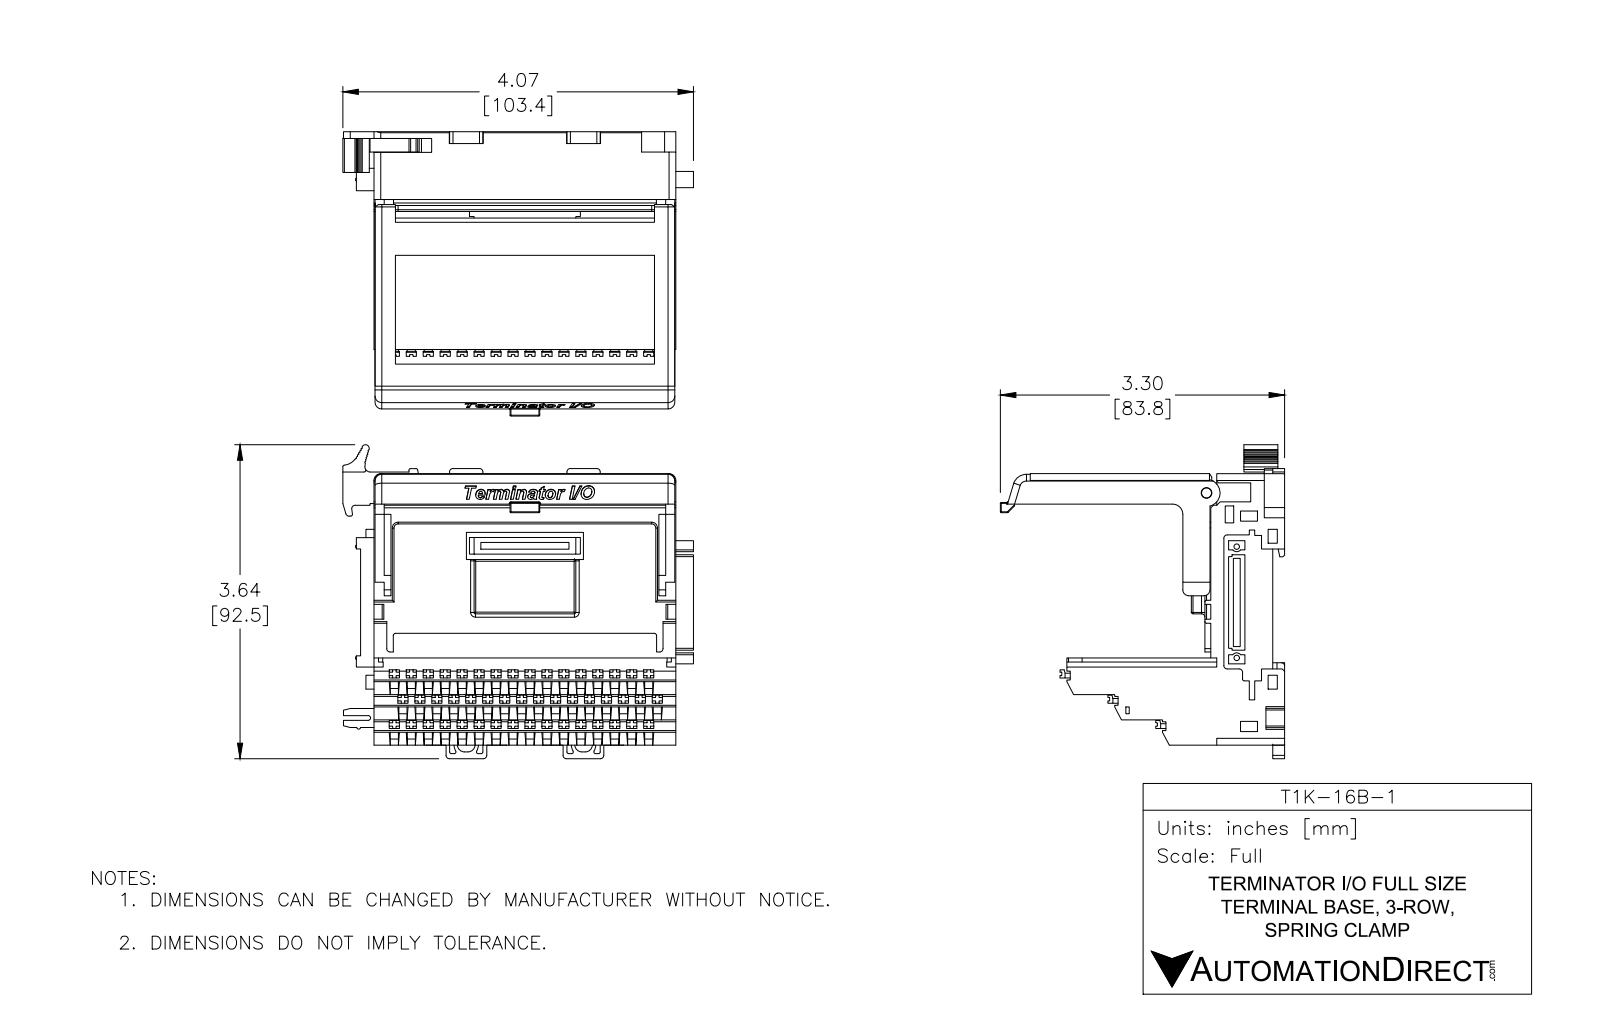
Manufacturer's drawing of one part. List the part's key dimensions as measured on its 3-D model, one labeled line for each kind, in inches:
Part name (STEP PRODUCT): T1K-16B-1
STEP written by: SolidWorks 2013 (AUTOMOTIVE_DESIGN)
Units: inches
Bodies: 16 solids, 1656 faces (1466 planar, 85 cylindrical, 105 other)
Overall size (bounding box): 4.075 × 3.625 × 3.235
Volume: 15.46 in³ · Surface area: 106.9 in²
Round holes (diameter × count): ⌀0.063 ×2
Round bosses / shafts (diameter × count): ⌀0.059 ×2
Partial cylindrical surfaces — rounded edges, fillets, slot ends (radius × count): R0.039 ×24, R0.079 ×17, R0.03 ×12, R0.081 ×4, R0.033 ×2, R0.08 ×2, R0.08 ×2, R0.138 ×1
Main face-to-face distances: 0.079, 0.138, 2.07, 0.661, 0.74, 0.878, 3.15, 0.799, 1.079, 3.504
Hole centre spacings: 1.329
